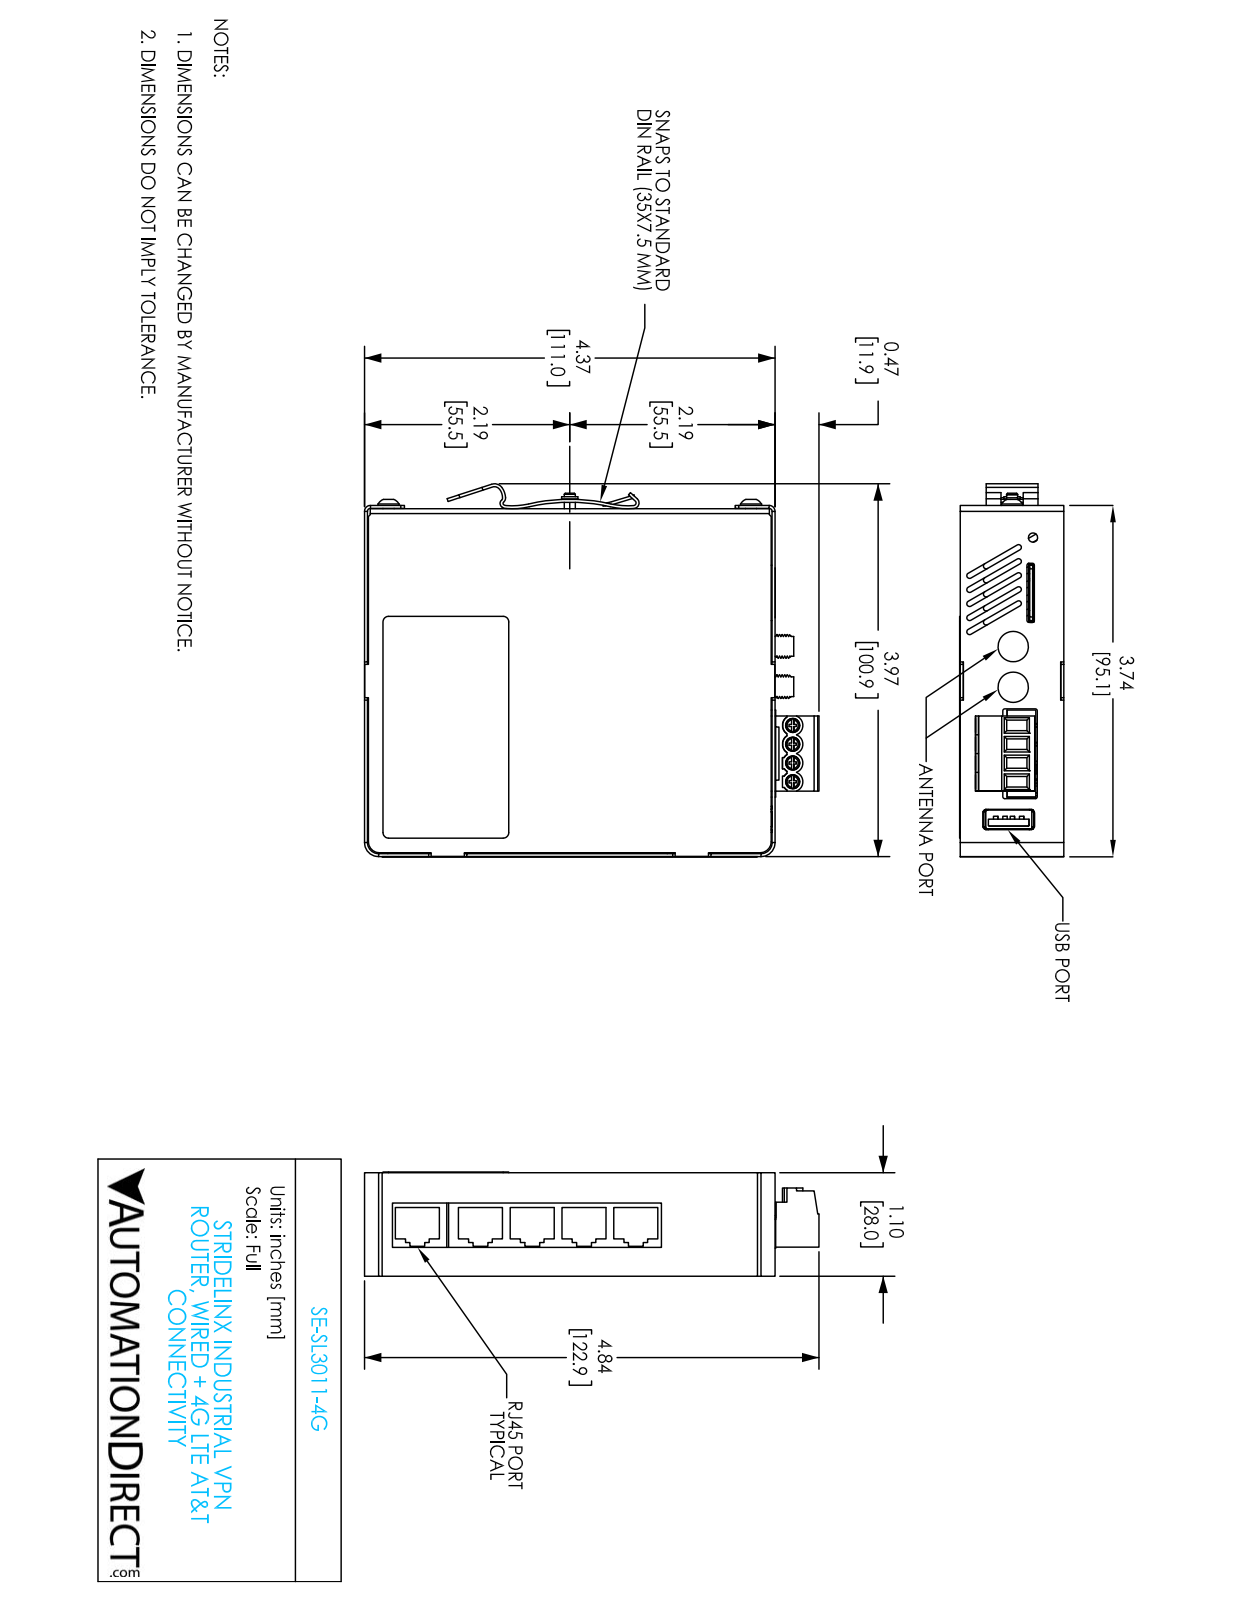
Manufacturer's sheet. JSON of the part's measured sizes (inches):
{"part_name": "base_C5_Assy; Extruded_1_3; X11_1; Cylinder_1 (+8 more)", "step_written_by": "SolidWorks 2017 (AUTOMOTIVE_DESIGN)", "units": "inches", "bodies": {"solids": 64, "faces": 2976, "planar": 2066, "cylindrical": 772, "other": 138}, "overall_size": [4.837, 3.973, 1.109], "volume_in3": 2.851, "surface_area_in2": 143.9, "round_holes": [[0.079, 6], [0.098, 4], [0.15, 4], [0.048, 2], [0.138, 2], [0.183, 2], [0.008, 1], [0.118, 1], [0.128, 1], [0.157, 1], [0.173, 1], [0.212, 1]], "round_bosses_or_shafts": [[0.028, 39], [0.224, 4], [0.143, 4], [0.124, 4], [0.118, 3], [0.312, 2], [0.25, 2], [0.21, 2]], "partial_cylinders_radius": [[0.004, 91], [0.006, 38], [0.008, 33], [0.03, 25], [0.01, 24], [0.039, 19], [0.02, 14], [0.024, 8]], "face_to_face_distances": [0.031, 1.071, 1.102, 1.039, 3.673, 4.339, 3.705, 0.038, 1.109, 1.078], "hole_center_spacings": [0.2, 0.1, 0.316, 0.3, 0.361, 0.4, 1.615, 1.711]}
